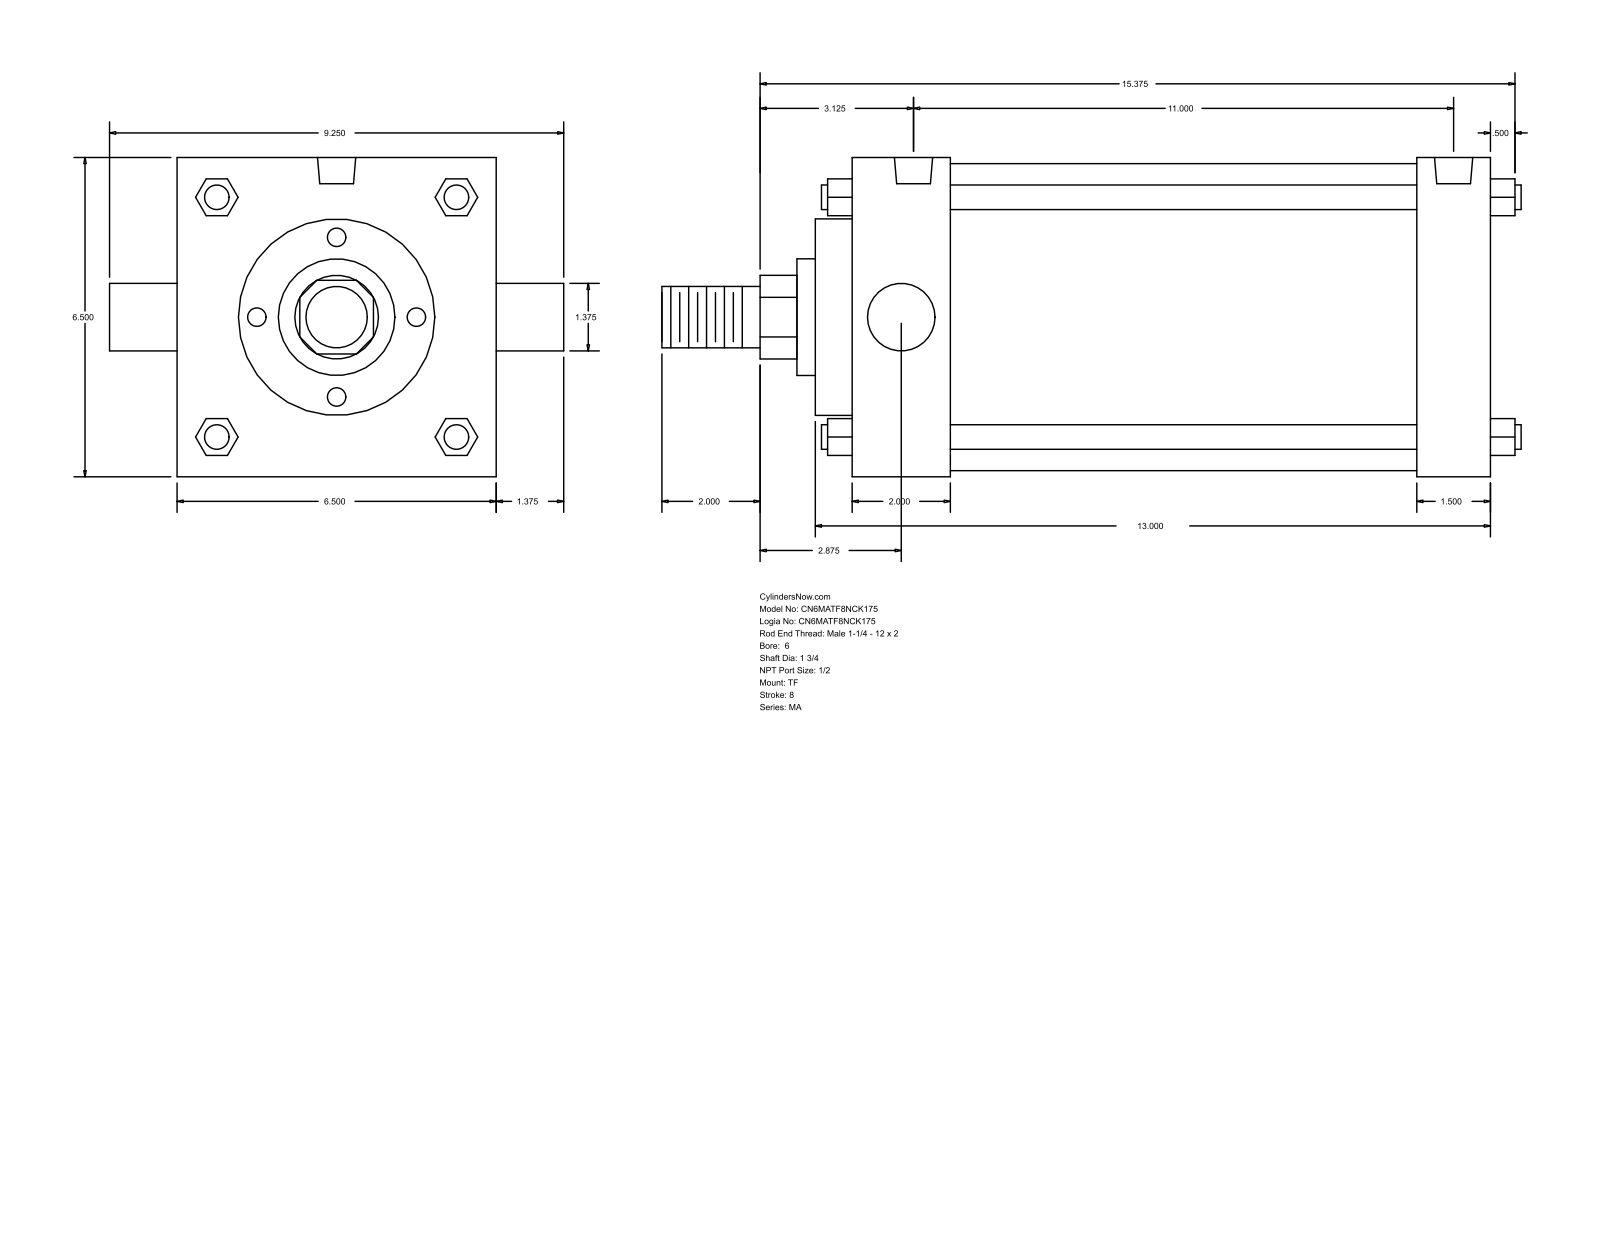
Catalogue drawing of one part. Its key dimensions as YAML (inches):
part_name: "MA_TF__0600_1.75"
step_written_by: "GSSL Pune (CONFIG_CONTROL_DESIGN)"
units: inches
bodies: {solids: 0, faces: 122, planar: 93, cylindrical: 29, other: 0}
overall_size: [17.5, 9.25, 6.5]
round_holes:
  - {diameter: 0.687, count: 3}
  - {diameter: 0.778, count: 2}
round_bosses_or_shafts:
  - {diameter: 0.5, count: 4}
  - {diameter: 6.25, count: 1}
  - {diameter: 4, count: 1}
  - {diameter: 2.375, count: 1}
  - {diameter: 1.75, count: 1}
  - {diameter: 1.375, count: 1}
  - {diameter: 1.25, count: 1}
partial_cylinders:
  - {radius: 0.852, count: 1}
face_to_face_distances: [6.5, 13, 0.75, 2, 11, 11.5, 9.5, 1.5, 2.75, 12.25]
hole_center_spacings: [11]
